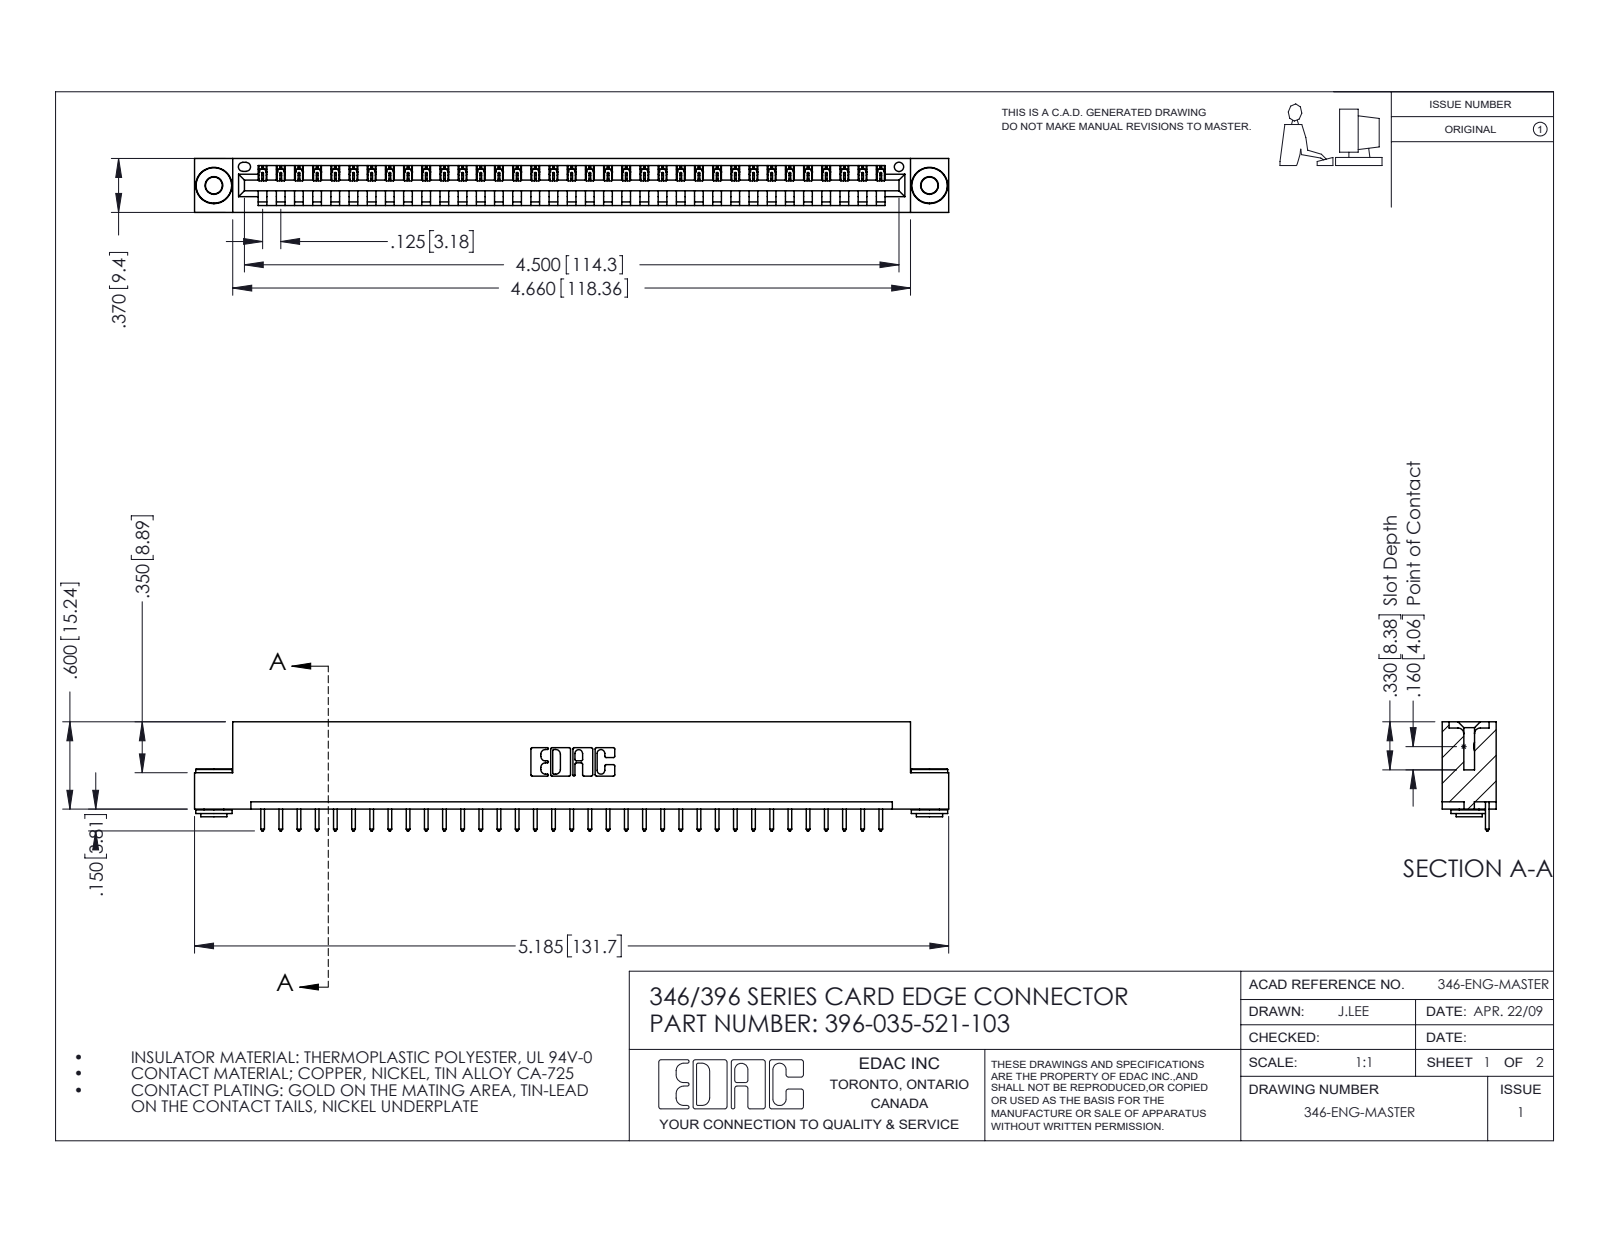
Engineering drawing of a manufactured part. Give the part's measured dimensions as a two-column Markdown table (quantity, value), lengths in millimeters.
| quantity | value |
| --- | --- |
| part name | 396-035-521-103; 345-292-001_345-293-121; 345-250-002_345-250-002-102; 346 Part_Flush Mounting Lugs - 0.156 Dia-TH |
| STEP written by | SolidWorks 2016 (CONFIG_CONTROL_DESIGN) |
| units | millimeters |
| bodies | 38 solids, 2190 faces (1486 planar, 696 cylindrical, 8 other) |
| overall size | 131.7 × 19.1 × 9.4 |
| volume | 12 500 mm³ |
| surface area | 15 340 mm² |
| round holes (diameter × count) | 2.9 × 2, 4 × 2, 1.6 × 1 |
| round bosses / shafts (diameter × count) | 6.4 × 2, 4.6 × 2, 3.5 × 2 |
| partial cylindrical surfaces (radius × count) | 0.2 × 70, 0.3 × 70, 0.3 × 22, 0.2 × 6, 0.8 × 6, 0.7 × 3, 0.8 × 2, 1 × 2 |
| main face-to-face distances | 1.2, 8.2, 9.4, 6.4, 0.6, 1.8, 7.6, 3.8, 5.6, 2.5 |
| hole center spacings | 6.2, 119.7, 125 |
